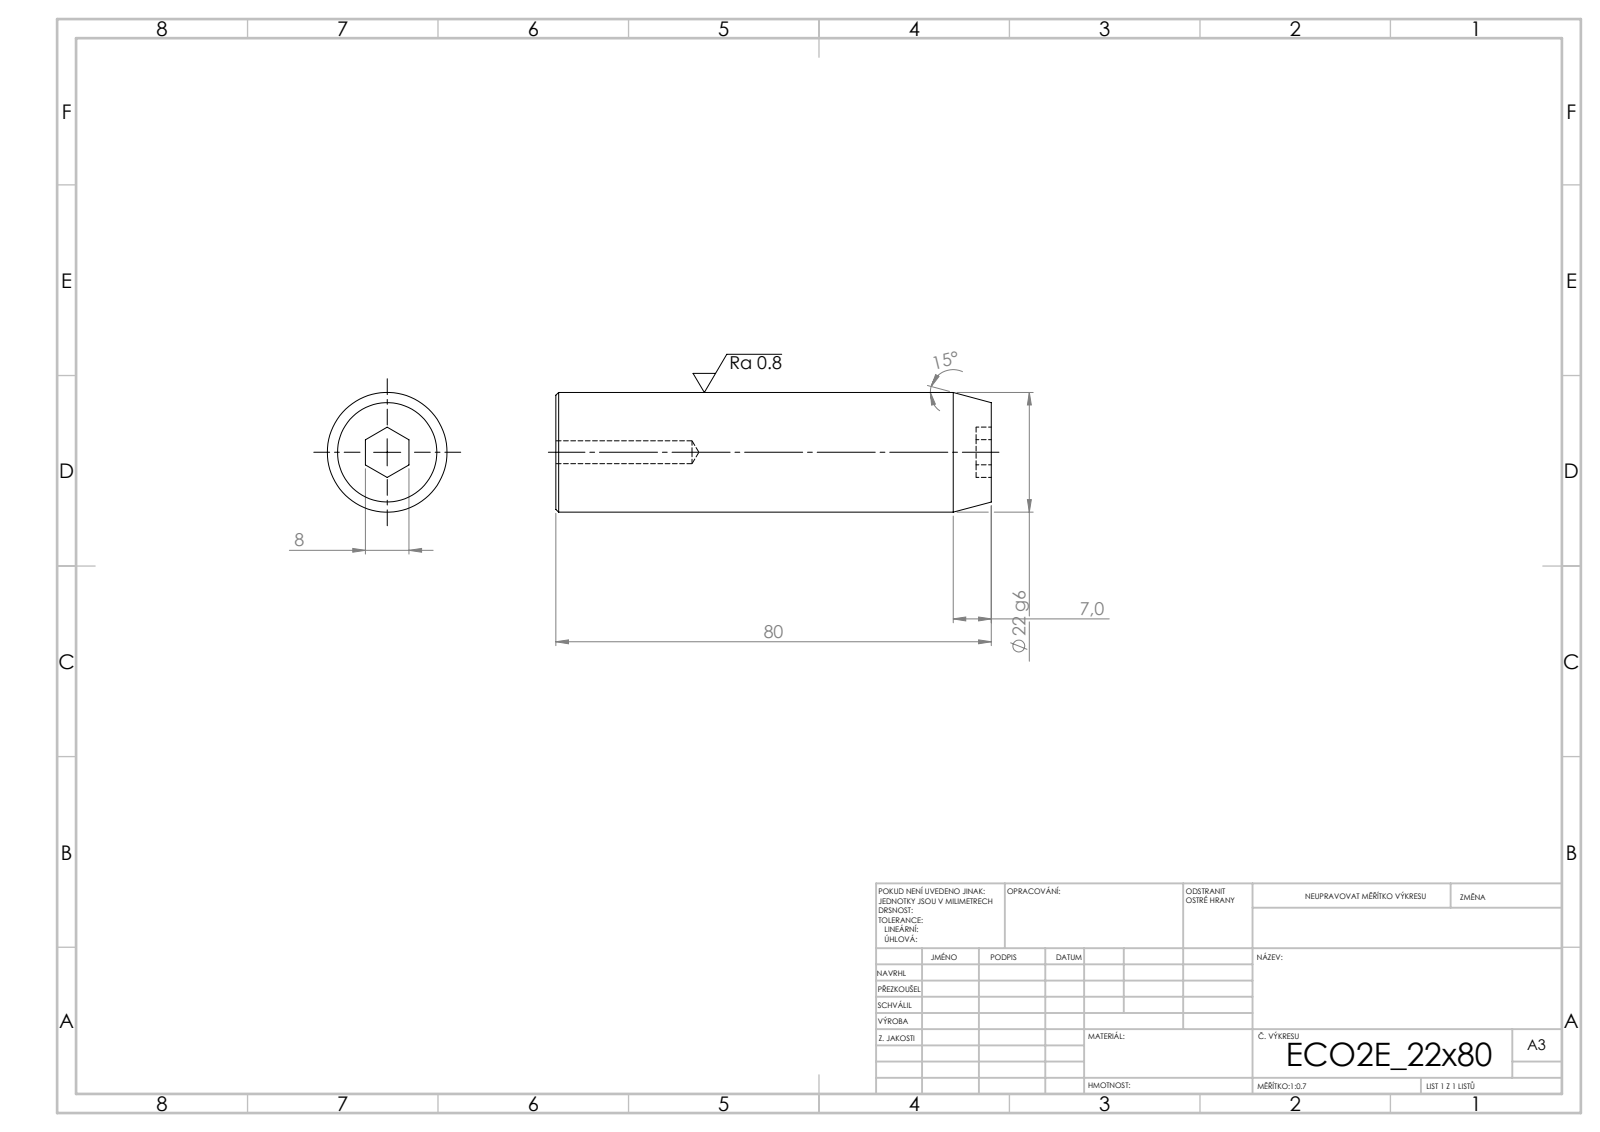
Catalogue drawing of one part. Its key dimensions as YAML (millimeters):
step_written_by: "SolidWorks 2019 (CONFIG_CONTROL_DESIGN)"
units: millimeters
bodies: {solids: 1, faces: 19, planar: 9, cylindrical: 4, other: 6}
overall_size: [80, 22, 22]
volume: 29467
surface_area: 6534
round_holes:
  - {diameter: 4.2, count: 1}
round_bosses_or_shafts:
  - {diameter: 22, count: 1}
face_to_face_distances: [80, 2.8, 77.2, 8]
